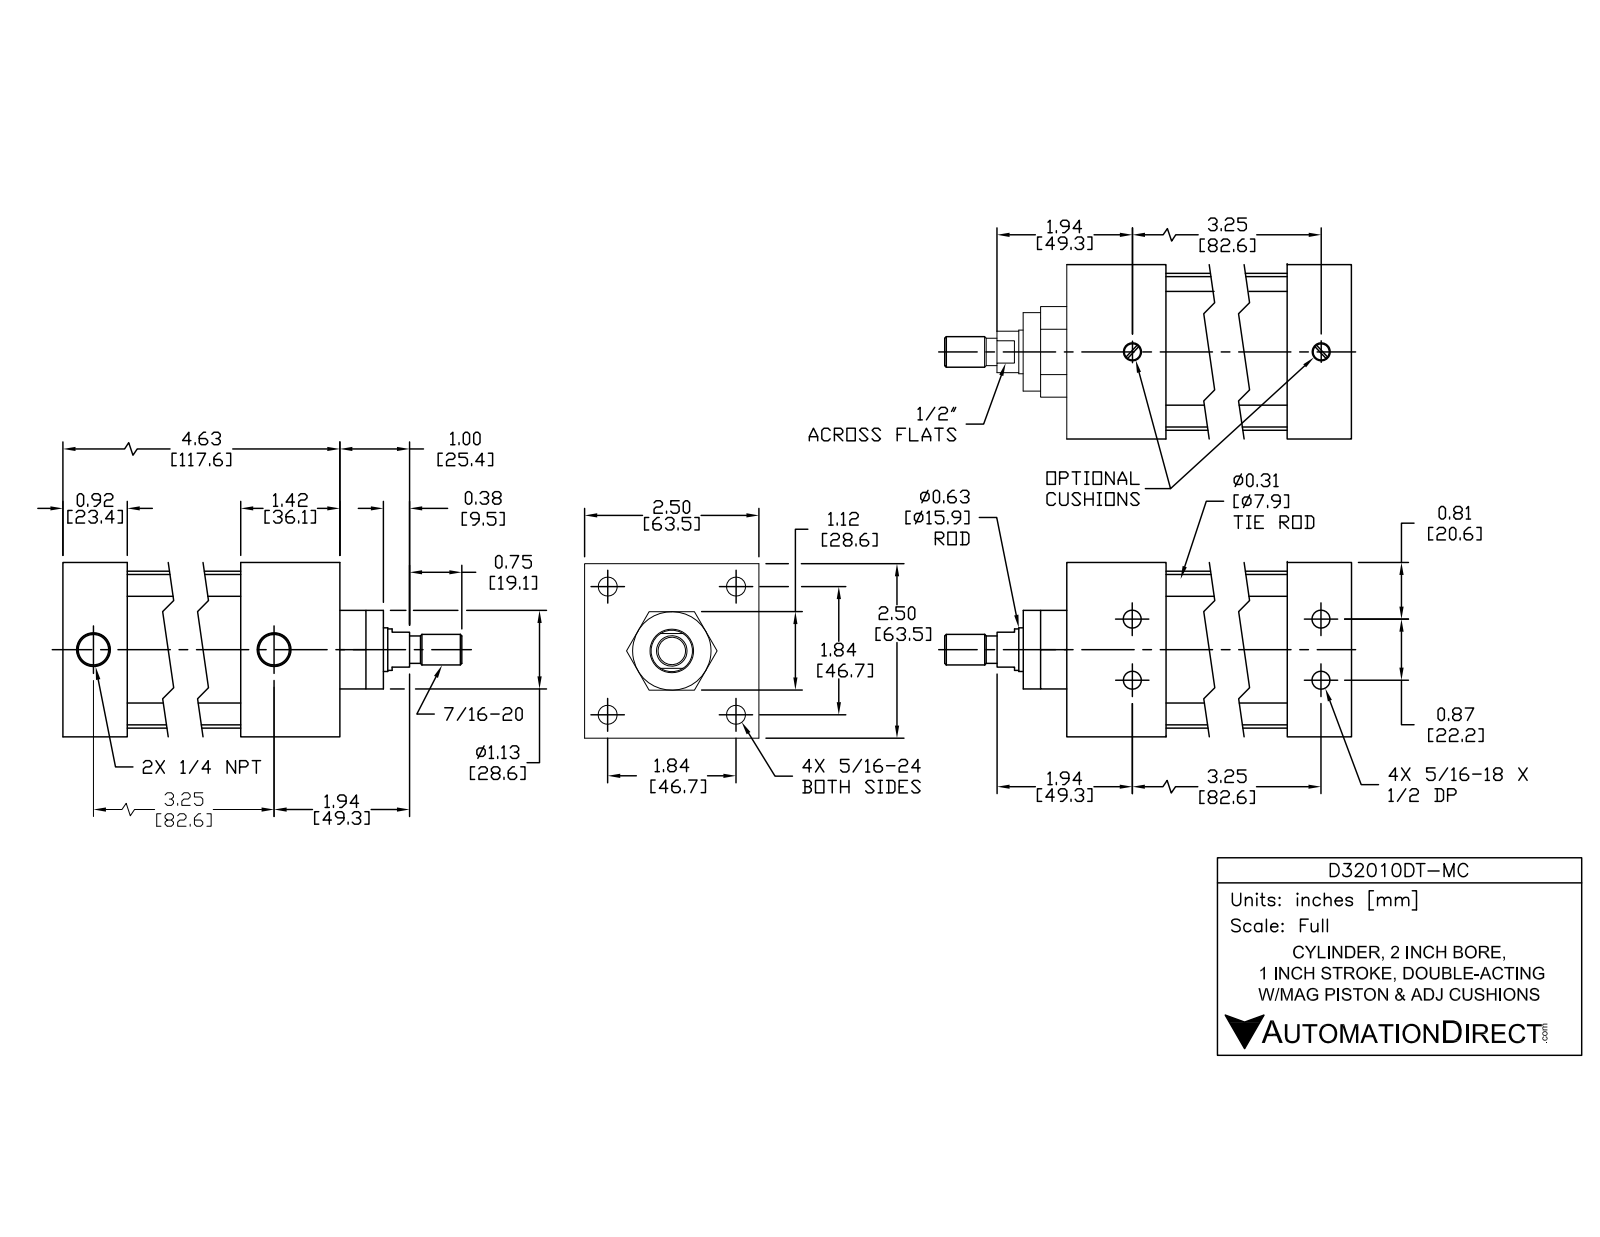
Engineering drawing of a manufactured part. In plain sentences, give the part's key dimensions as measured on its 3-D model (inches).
The part is named "D32010DT-MC; D32010DT-M PISTON; D32010DT-M BODY". Its 3-D file was written by "SolidWorks 2015 (AUTOMOTIVE_DESIGN)". It is 12 solids with 298 faces: 94 planar, 114 cylindrical and 90 other. Overall it measures 6.371 by 2.5 by 2.5 inches. Its volume is 21.22 cubic inches and its surface area 142.4 square inches. Round holes: 4 of diameter 0.252, 4 of diameter 0.267, 4 of diameter 0.359, 4 of diameter 0.5, 2 of diameter 0.297, 2 of diameter 0.477, 1 of diameter 0.625, 1 of diameter 0.628, 1 of diameter 2. Round bosses or shafts: 4 of diameter 0.484, 4 of diameter 0.313, 4 of diameter 0.282, 1 of diameter 2.25, 1 of diameter 1.997, 1 of diameter 1.12, 1 of diameter 0.622, 1 of diameter 0.59. Partial cylindrical surfaces (rounded edges, fillets, slot ends): 4 of radius 0.25. The main face-to-face distances are 2.5, 0.08, 2.201, 4.621, 1.42, 3.201, 2.281, 3.701, 0.92, 1. The hole center spacings are 0.437, 1.307, 1.848, 3.274, 3.245, 0.875, 2.613, 3.361.
